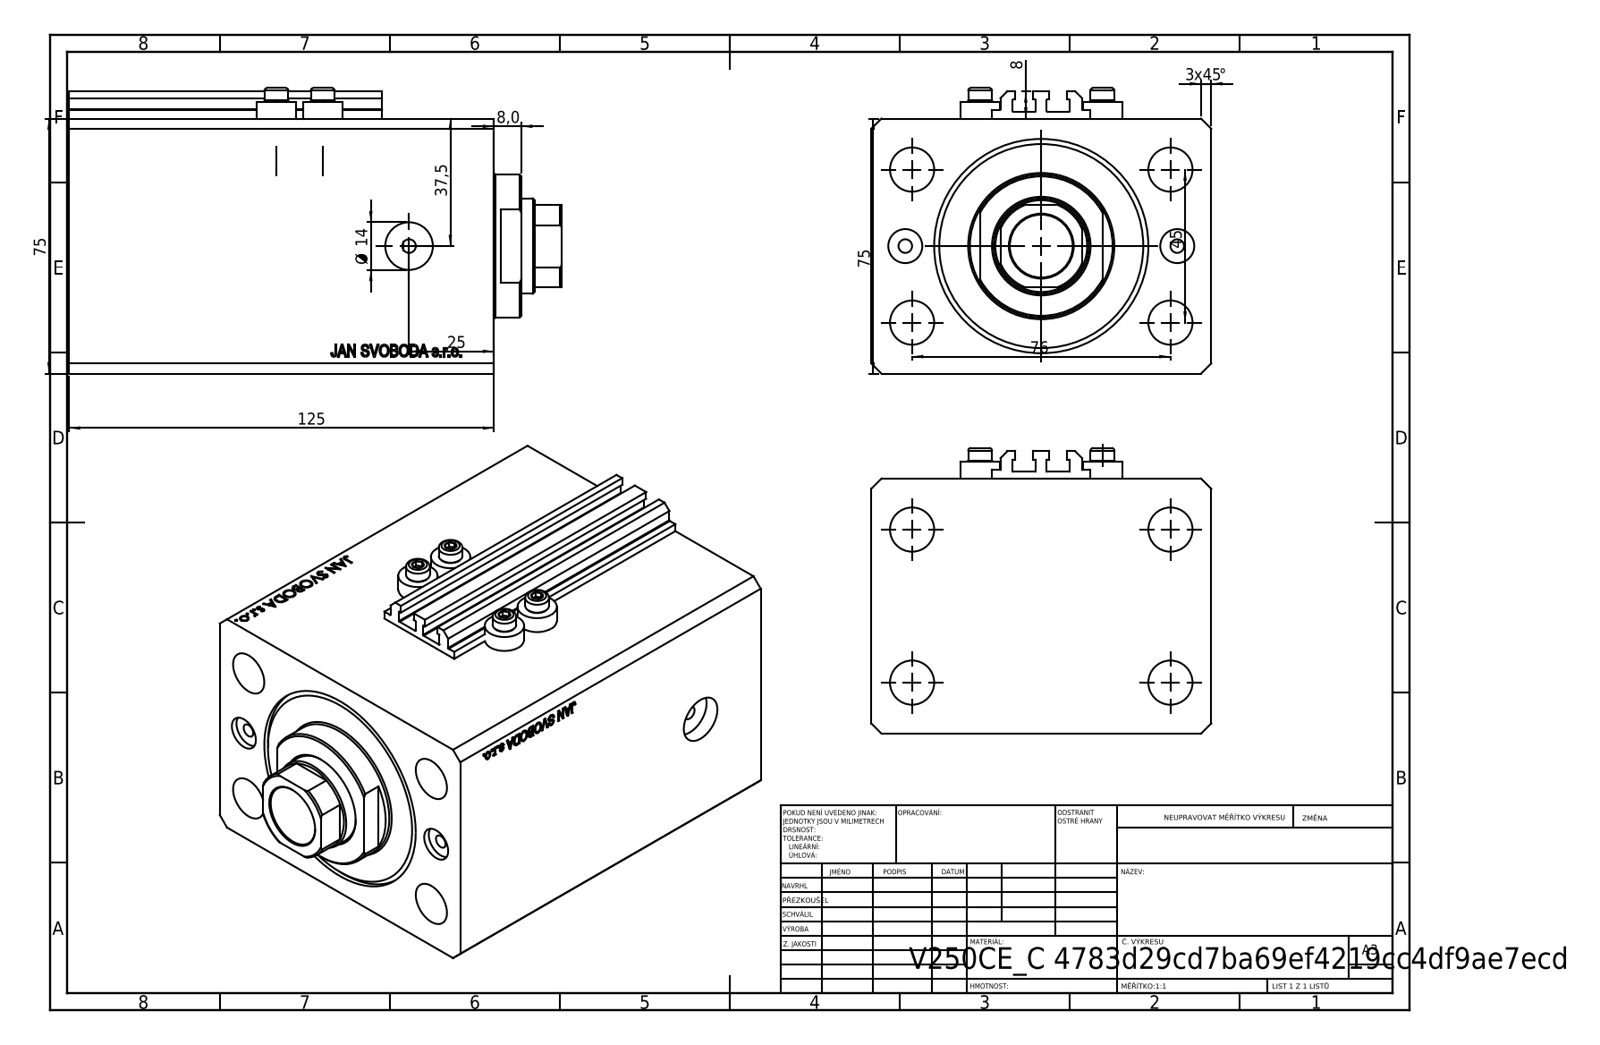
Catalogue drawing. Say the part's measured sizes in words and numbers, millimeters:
The part is named "V250CE_C_Body; ALLEN BOLT V250CE; V250CE_VC_C; V250CE_C_VCP". Its 3-D file was written by "SolidWorks 2019 (CONFIG_CONTROL_DESIGN)". It is 8 solids with 1034 faces: 504 planar, 86 cylindrical and 444 other. Overall it measures 144.9 by 100 by 84 millimeters. Its volume is 819 897 cubic millimeters and its surface area 144 282 square millimeters. Round holes: 8 of diameter 4, 4 of diameter 13, 2 of diameter 10, 2 of diameter 14, 1 of diameter 18.5, 1 of diameter 28, 1 of diameter 50, 1 of diameter 63. Round bosses or shafts: 4 of diameter 11.6, 4 of diameter 7, 1 of diameter 42. Partial cylindrical surfaces (rounded edges, fillets, slot ends): 10 of radius 0.2, 1 of radius 13.5. The main face-to-face distances are 75, 100, 125, 11.9, 113.1, 98.4, 86.5, 26.6, 48.4, 8. The hole center spacings are 22.59, 44.16, 81.18, 13.6, 36, 38.48, 40, 45.
